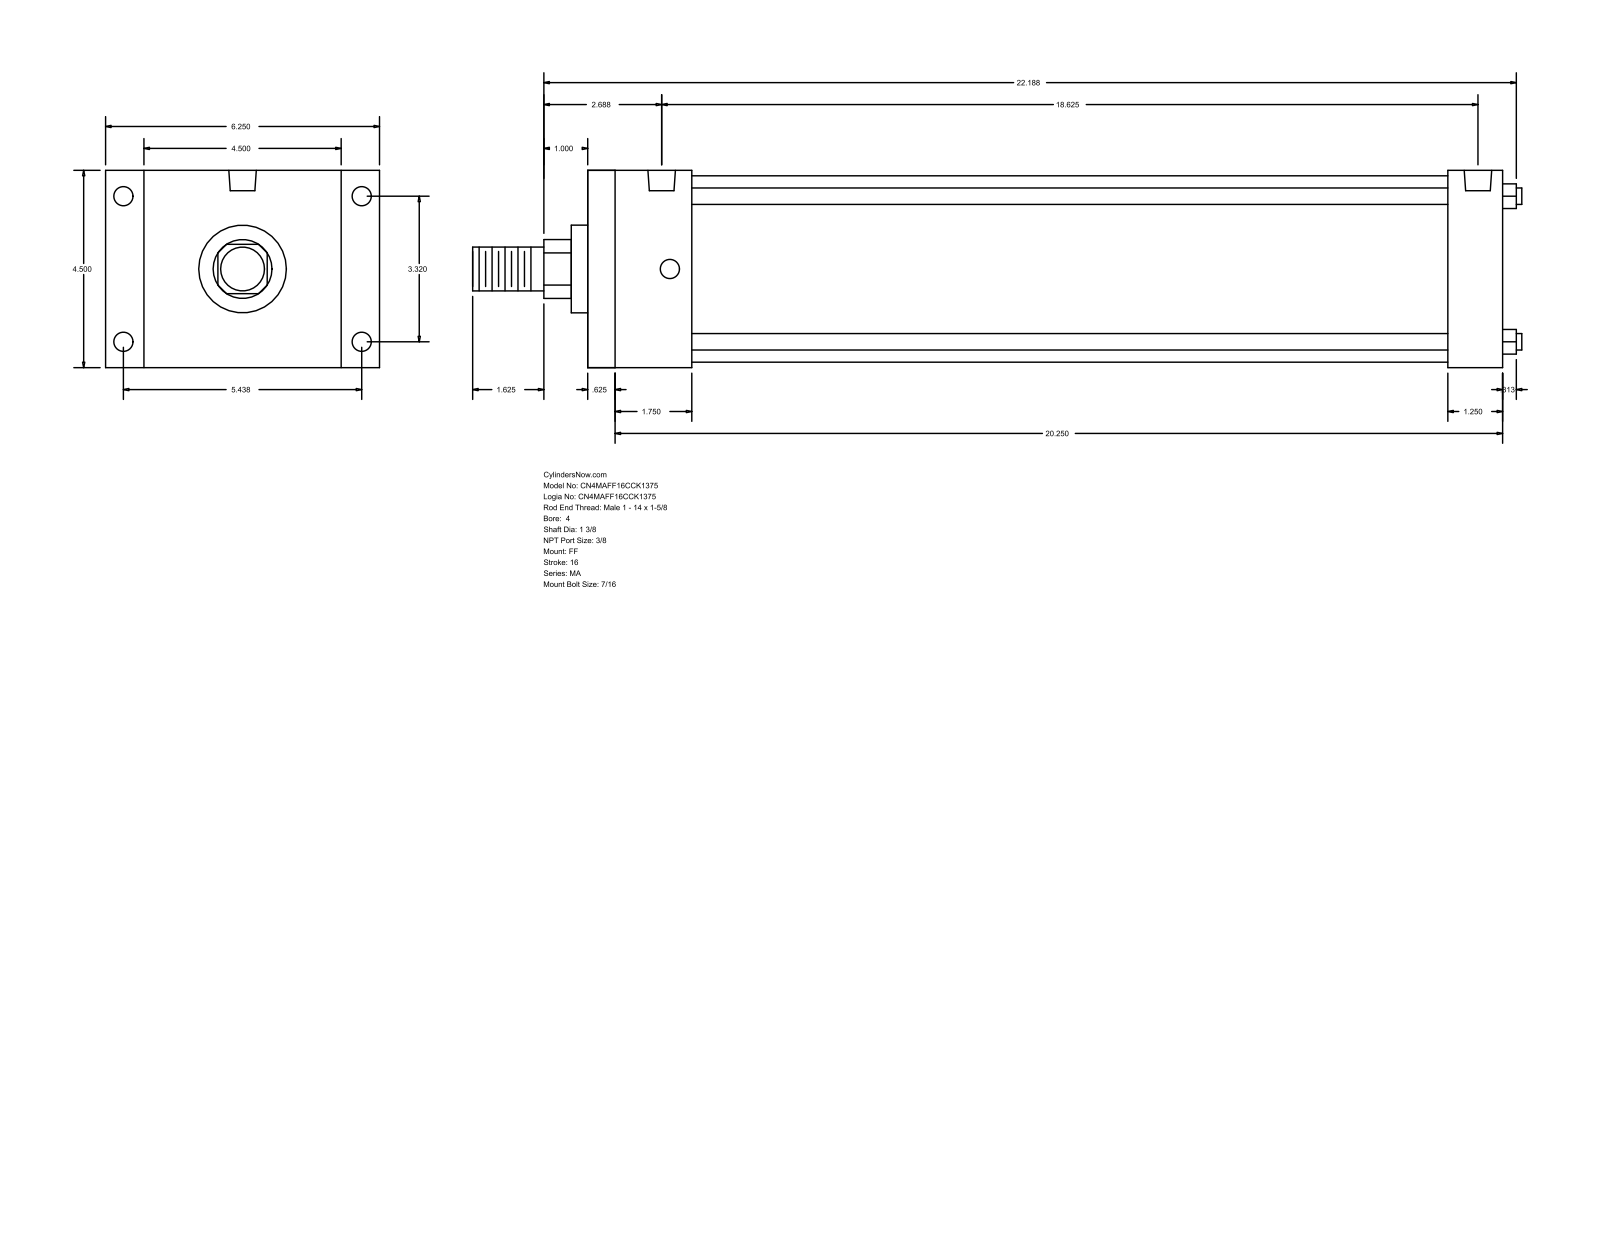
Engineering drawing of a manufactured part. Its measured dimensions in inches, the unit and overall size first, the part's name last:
Units: inches
Overall size (bounding box): 23.937 × 6.25 × 4.5
Round holes (diameter × count): ⌀0.437 ×8, ⌀0.627 ×2
Round bosses / shafts (diameter × count): ⌀0.375 ×4, ⌀4.25 ×1, ⌀2 ×1, ⌀1.375 ×1, ⌀1 ×1
Partial cylindrical surfaces — rounded edges, fillets, slot ends (radius × count): R0.672 ×1
Main face-to-face distances: 4.5, 20.875, 0.625, 20.25, 0.875, 5.375, 19.625, 19, 1.25, 2.375
Hole centre spacings: 3.32, 5.438, 6.371, 18.25, 0.187, 0.188, 18.437, 18.438
Bodies: 0 solids, 92 faces (64 planar, 28 cylindrical, 0 other)
Part name (STEP PRODUCT): MA_FF__0400_1.375
STEP written by: GSSL Pune (CONFIG_CONTROL_DESIGN)
